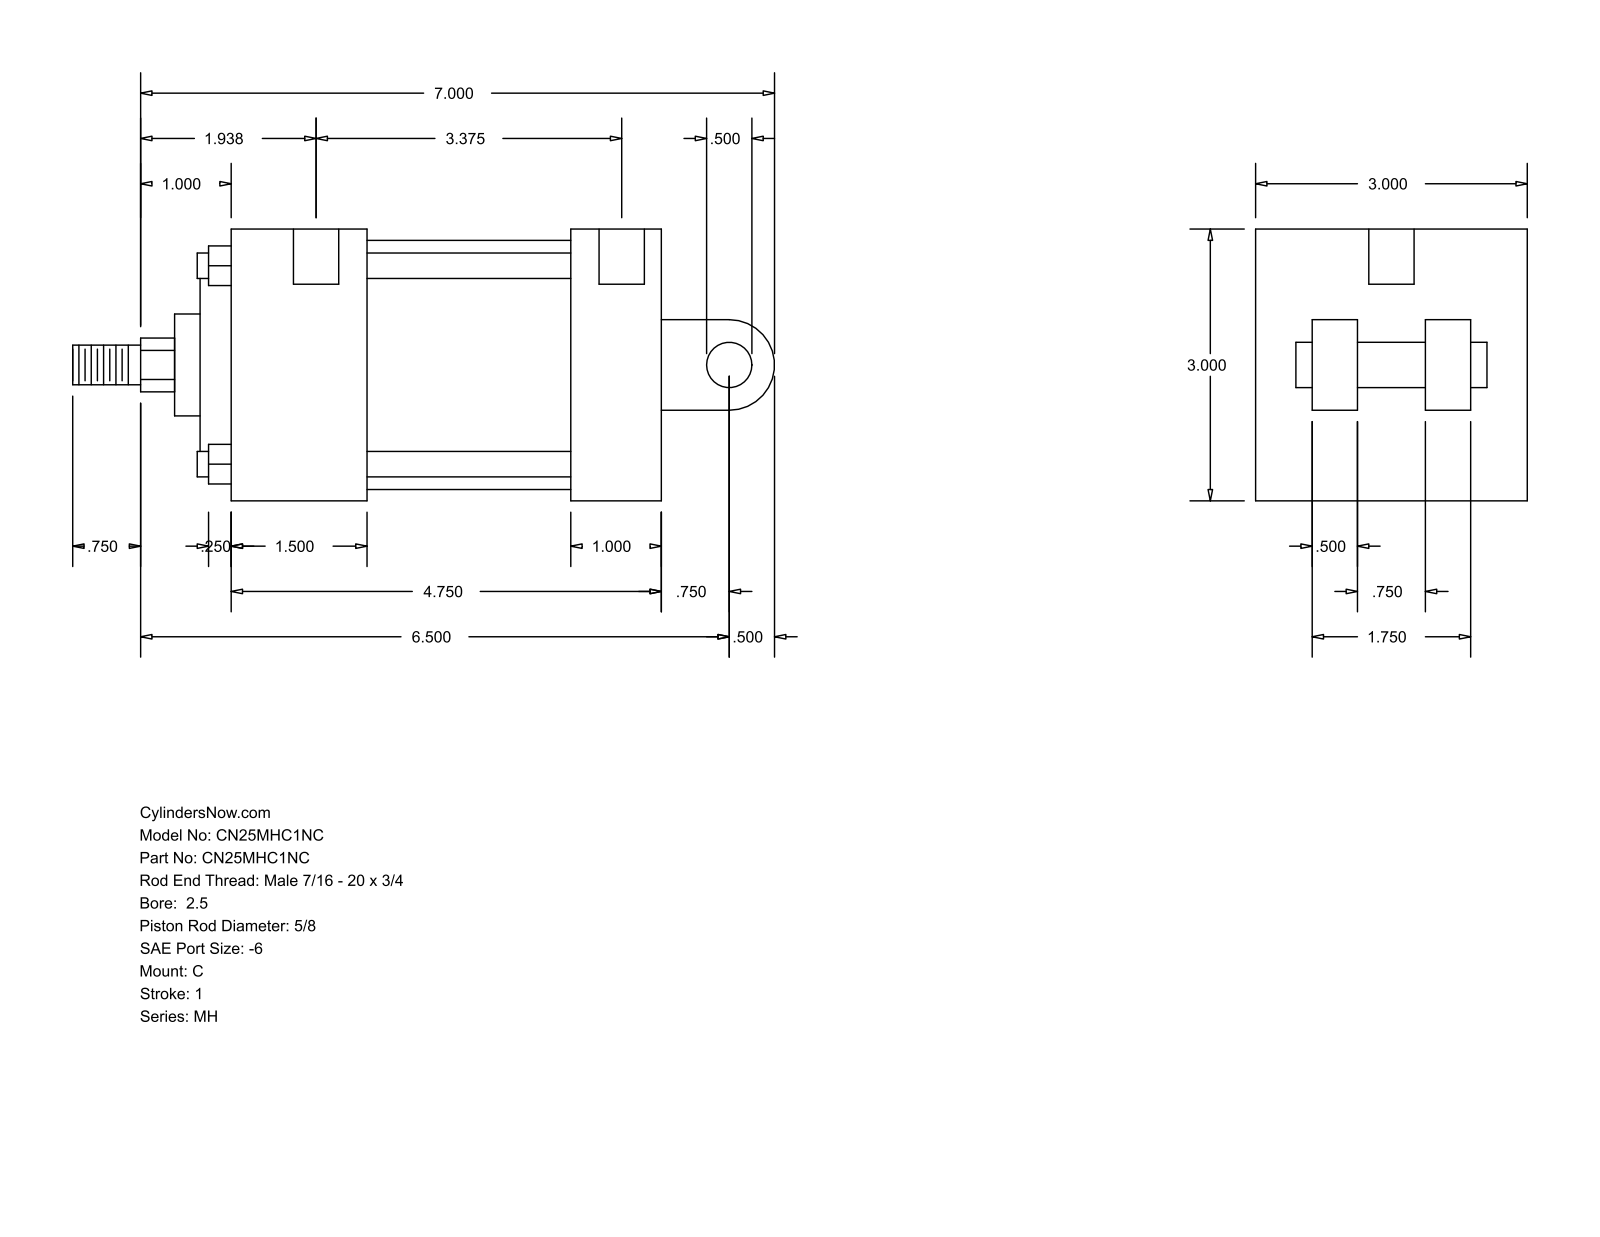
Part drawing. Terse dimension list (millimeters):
name: MH_C__0250_0.625
written by: GSSL Pune (CONFIG_CONTROL_DESIGN)
unit: mm
bodies: 0 solids, 101 faces (71 planar, 30 cylindrical, 0 other)
size: 196.85 × 76.2 × 76.2
holes: 4× ⌀5.56, 2× ⌀12.7
bosses: 4× ⌀7.14, 1× ⌀69.85, 1× ⌀55.55, 1× ⌀28.57, 1× ⌀15.88, 1× ⌀12.7, 1× ⌀11.11
rounds: 1× R7.54, 1× R12.7
face distances: 76.2, 25.4, 120.65, 15.87, 38.1, 82.55, 57.15, 95.25, 8.73, 46.83
hole spacings: 93.66, 3.17, 4.76, 85.73, 88.9, 90.49
